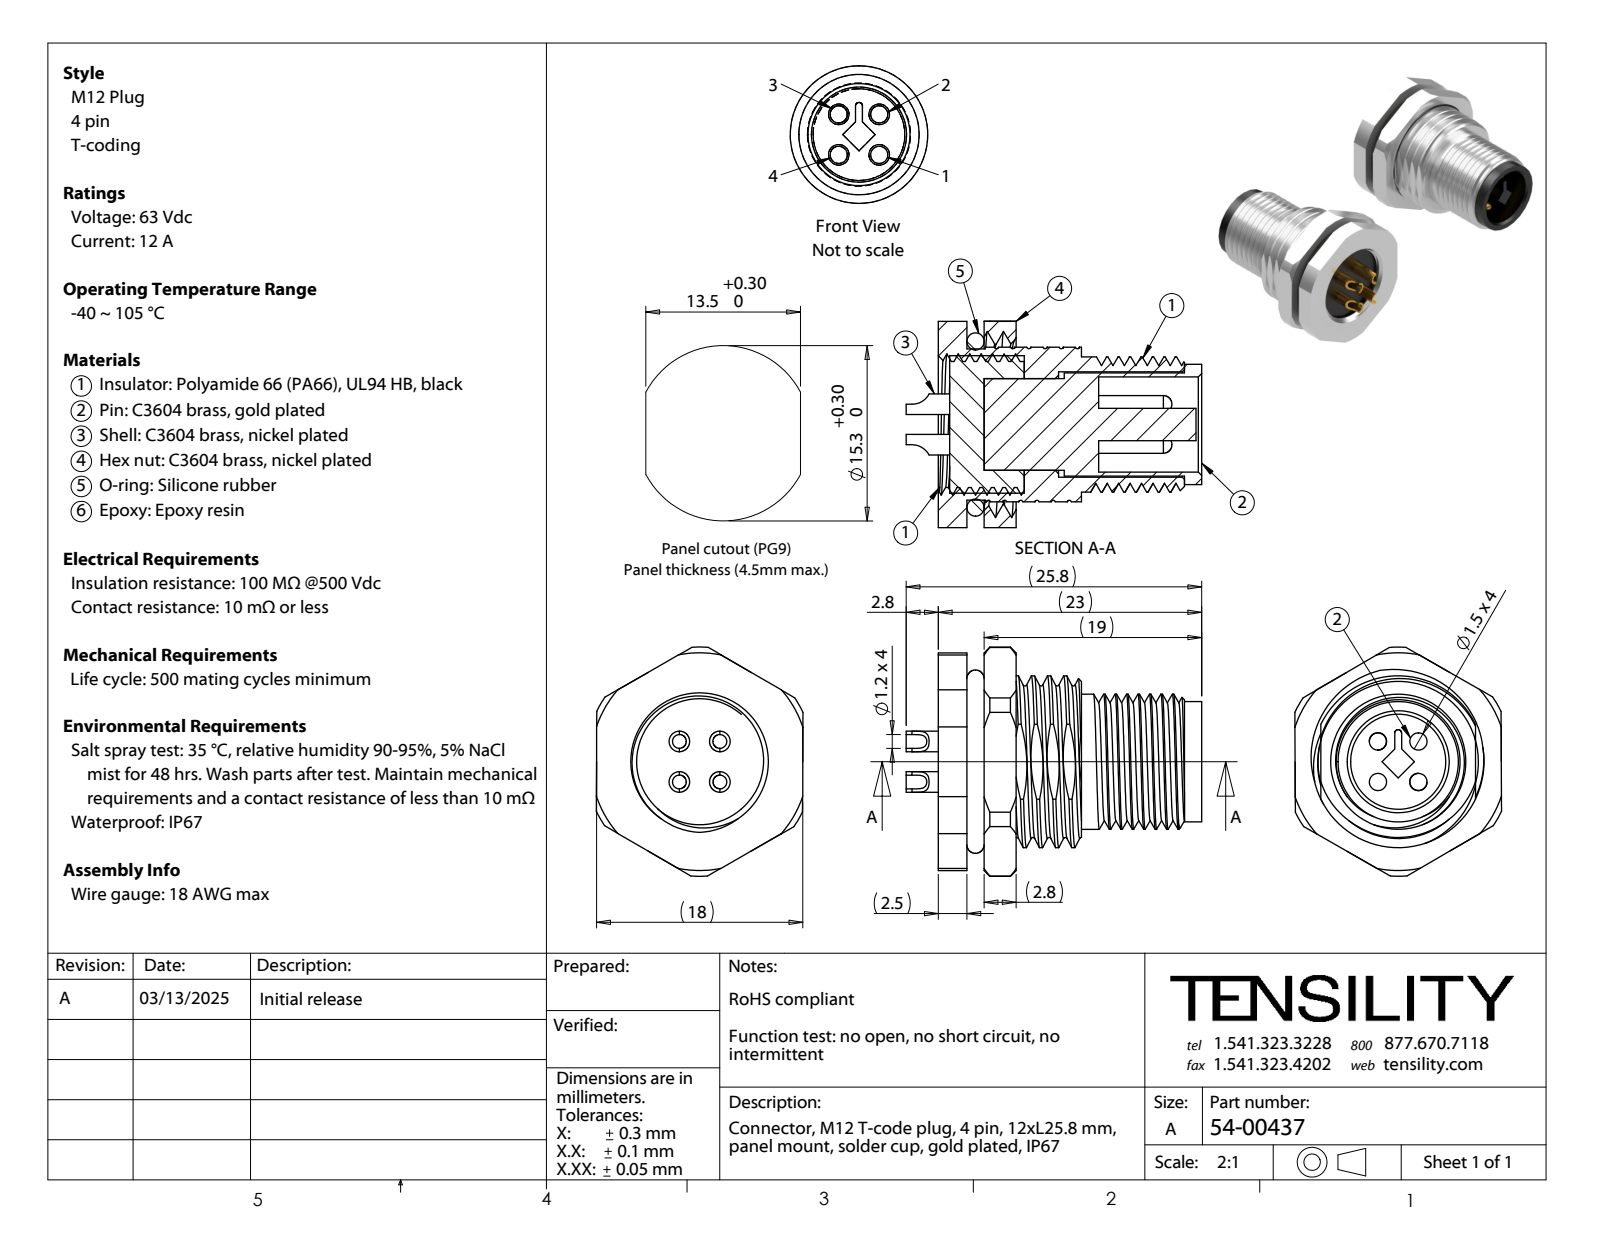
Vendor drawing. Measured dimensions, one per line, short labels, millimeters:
name: 54-00437-02; 54-00437-01; 54-00437-03; 54-00437-05 (+3 more)
written by: SolidWorks 2021 (CONFIG_CONTROL_DESIGN)
unit: mm
bodies: 9 solids, 334 faces (85 planar, 153 cylindrical, 96 other)
size: 25.8 × 20 × 18.04
volume: 3 096 mm³; area: 5 871 mm²
holes: 4× ⌀1.2, 4× ⌀1.5, 1× ⌀8, 1× ⌀8.3, 1× ⌀9.2, 1× ⌀11, 1× ⌀14
bosses: 4× ⌀1.8, 1× ⌀13.2, 1× ⌀12, 1× ⌀11.8, 1× ⌀10.5, 1× ⌀9
rounds: 2× R1.7, 1× R0.3, 1× R7.5, 1× R9.5, 1× R10
face distances: 1.5, 4, 6.5, 5, 7.5, 2.5, 3.5, 3, 1, 10
hole spacings: 2.5, 3.54, 5.01
